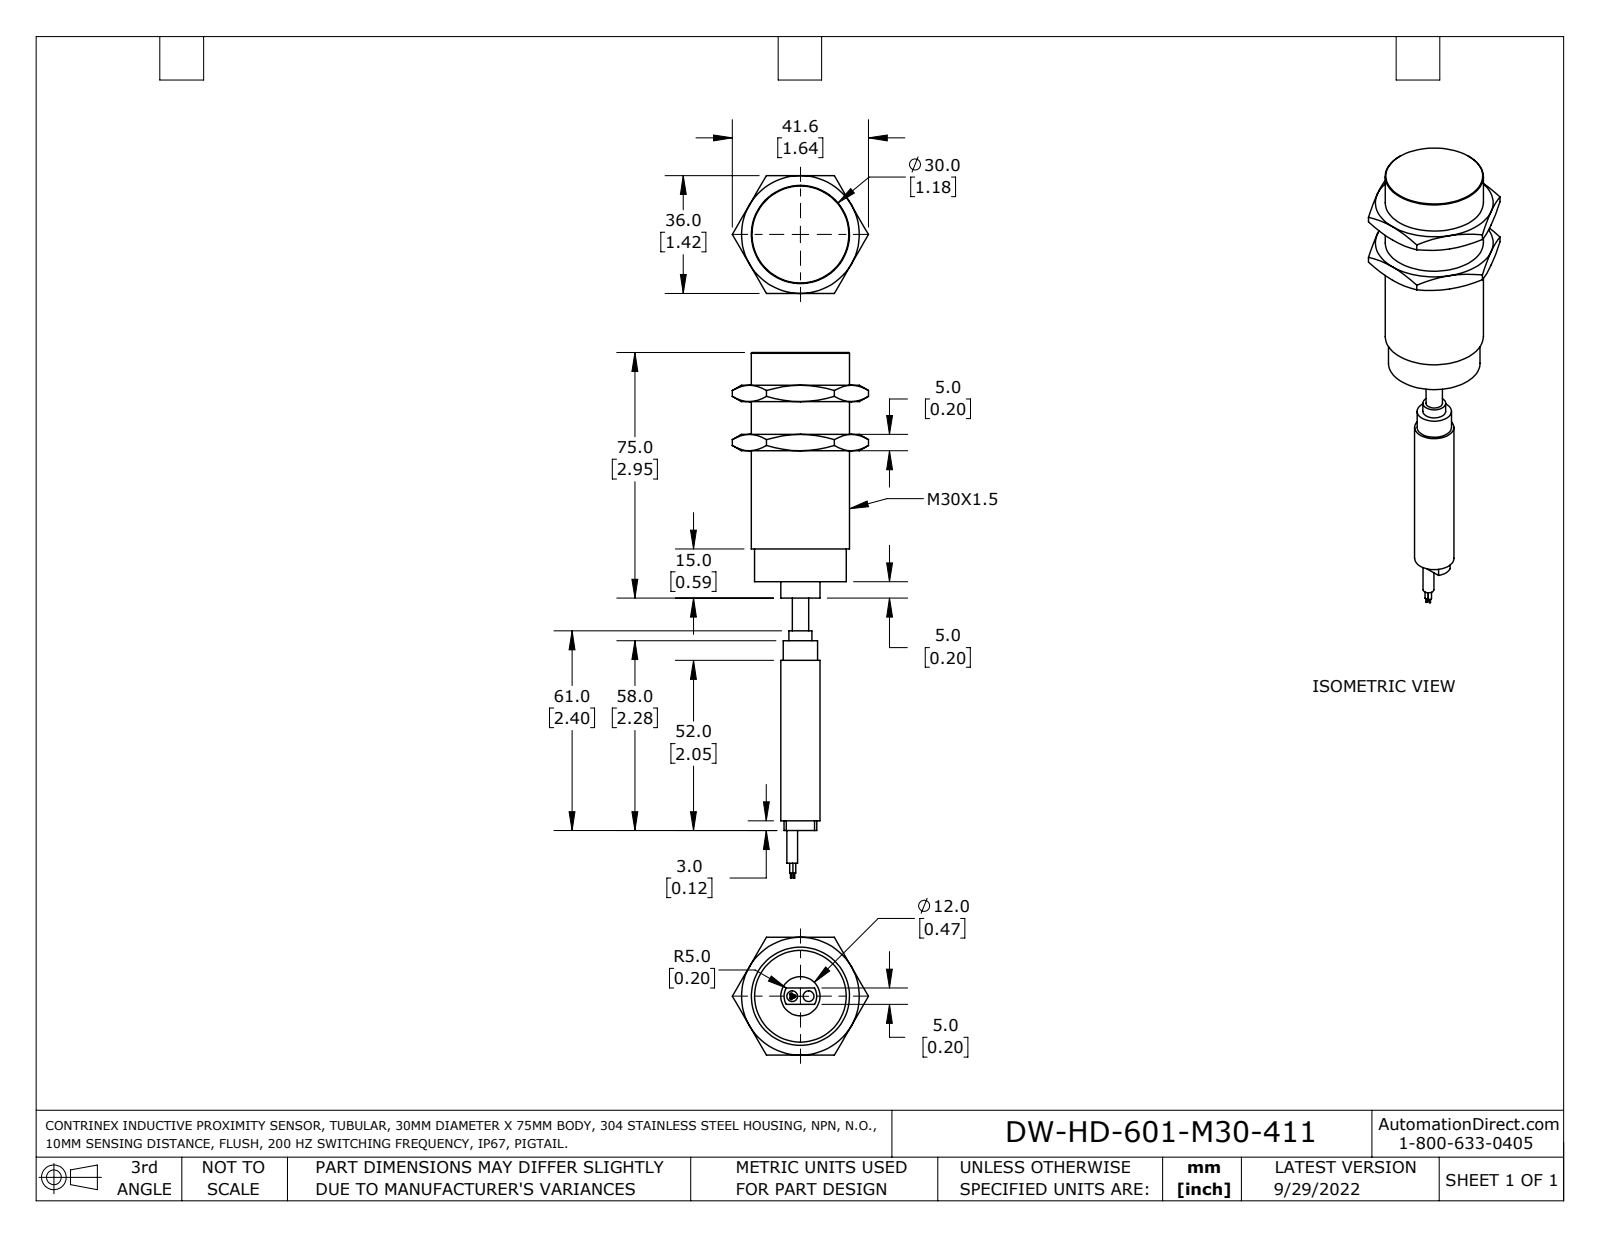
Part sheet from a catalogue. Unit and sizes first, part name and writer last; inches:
Units: inches
Overall size (bounding box): 6.319 × 1.637 × 1.417
Round holes (diameter × count): ⌀0.13 ×1
Round bosses / shafts (diameter × count): ⌀0.039 ×3, ⌀0.016 ×3, ⌀1.181 ×1, ⌀1.102 ×1, ⌀0.472 ×1, ⌀0.413 ×1, ⌀0.276 ×1, ⌀0.197 ×1
Partial cylindrical surfaces — rounded edges, fillets, slot ends (radius × count): R0.197 ×1
Main face-to-face distances: 0.591, 0.197, 0.394, 2.756, 2.362, 1.772, 1.417, 1.181, 2.165, 0.984
Volume: 3.641 in³ · Surface area: 19.51 in²
Bodies: 1 solid, 79 faces (35 planar, 19 cylindrical, 25 other)
Part name (STEP PRODUCT): DW-HD-601-M30-411
STEP written by: SolidWorks 2021 (AUTOMOTIVE_DESIGN)
